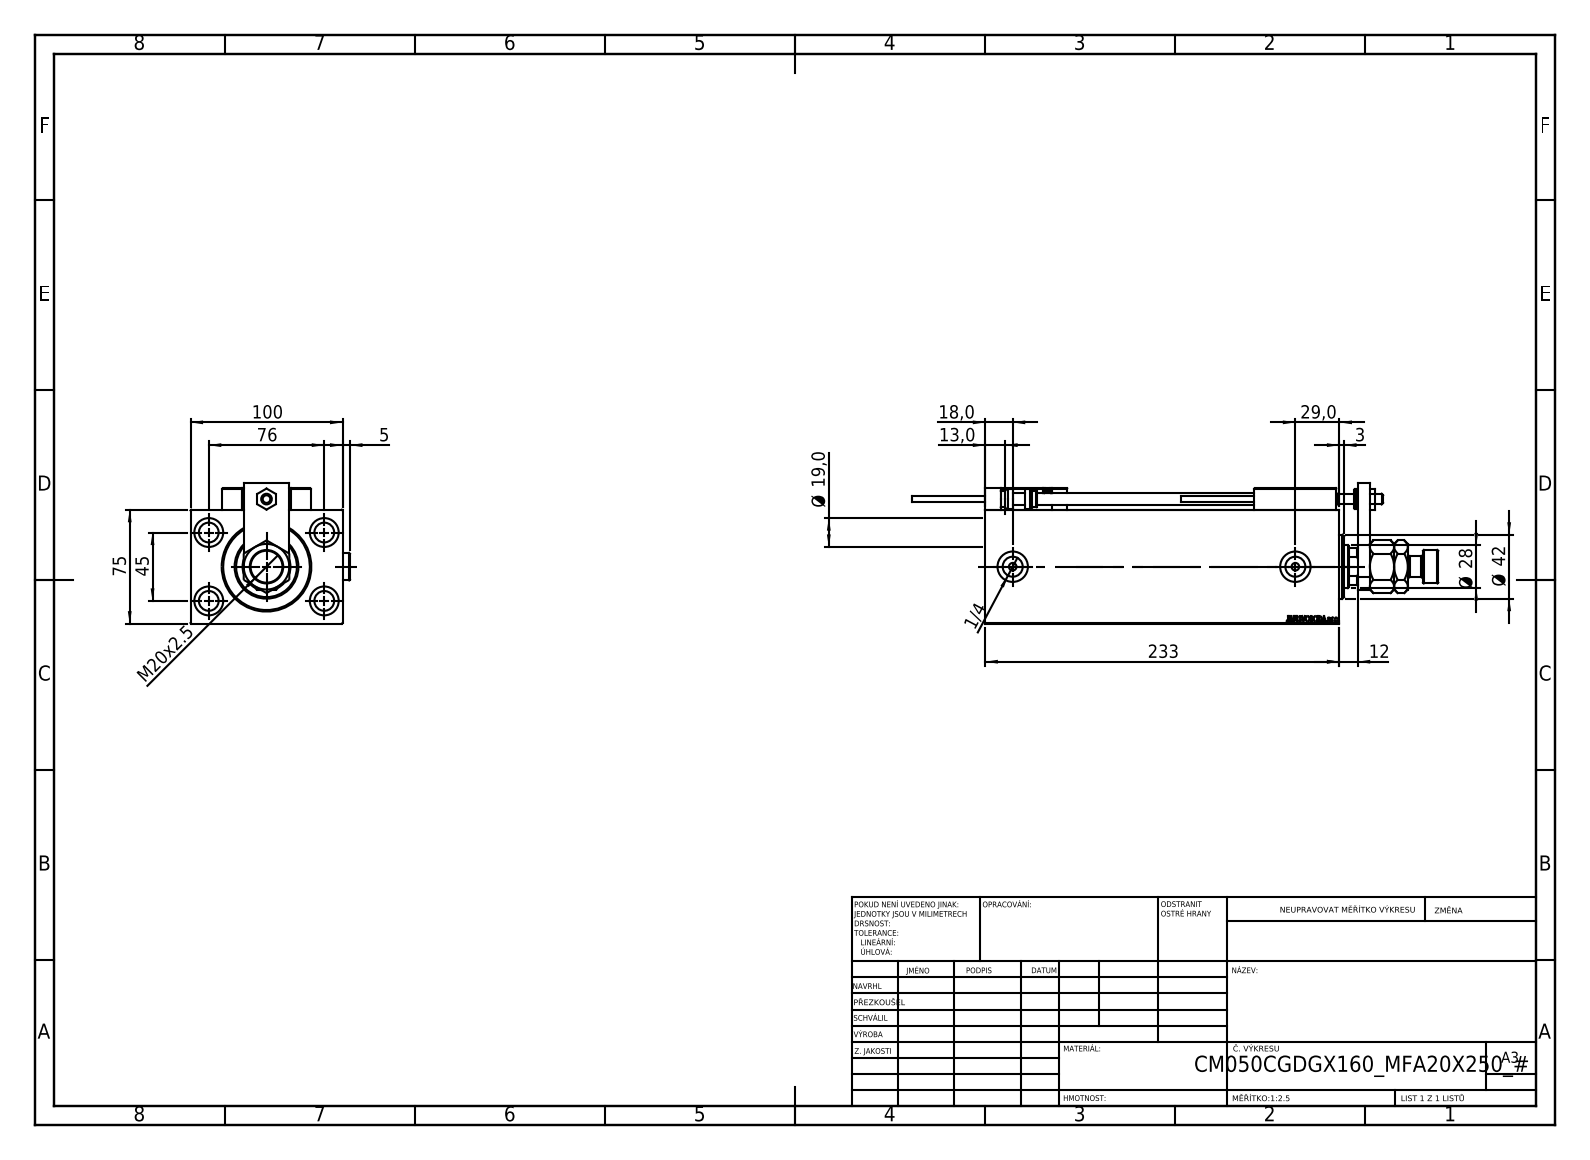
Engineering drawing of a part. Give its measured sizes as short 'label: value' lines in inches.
name: V450CM_C_VCP; ALLEN BOLT D5; KONCOVKA; ALLEN BOLT D8 (+8 more)
written by: SolidWorks 2019 (CONFIG_CONTROL_DESIGN)
unit: in
bodies: 26 solids, 1391 faces (611 planar, 210 cylindrical, 570 other)
size: 13.622 × 4.13 × 3.642
volume: 90.01 in³; area: 382 in²
holes: 5× ⌀0.315, 4× ⌀0.126, 4× ⌀0.157, 4× ⌀0.197, 4× ⌀0.512, 4× ⌀0.748, 3× ⌀0.787, 2× ⌀0.518, 1× ⌀0.276, 1× ⌀0.728, 1× ⌀1.102, 1× ⌀1.24
bosses: 2× ⌀0.709, 2× ⌀0.197, 2× ⌀0.15, 1× ⌀1.654, 1× ⌀0.866, 1× ⌀0.551, 1× ⌀0.512, 1× ⌀0.433
rounds: 30× R0.012, 2× R0.118, 1× R0.531
face distances: 2.953, 3.937, 0.551, 9.173, 0.472, 8.622, 0.787, 0.315, 0.945, 0.984
hole spacings: 1.739, 0.448, 0.787, 1.165, 1.169, 1.42, 1.661, 1.729
